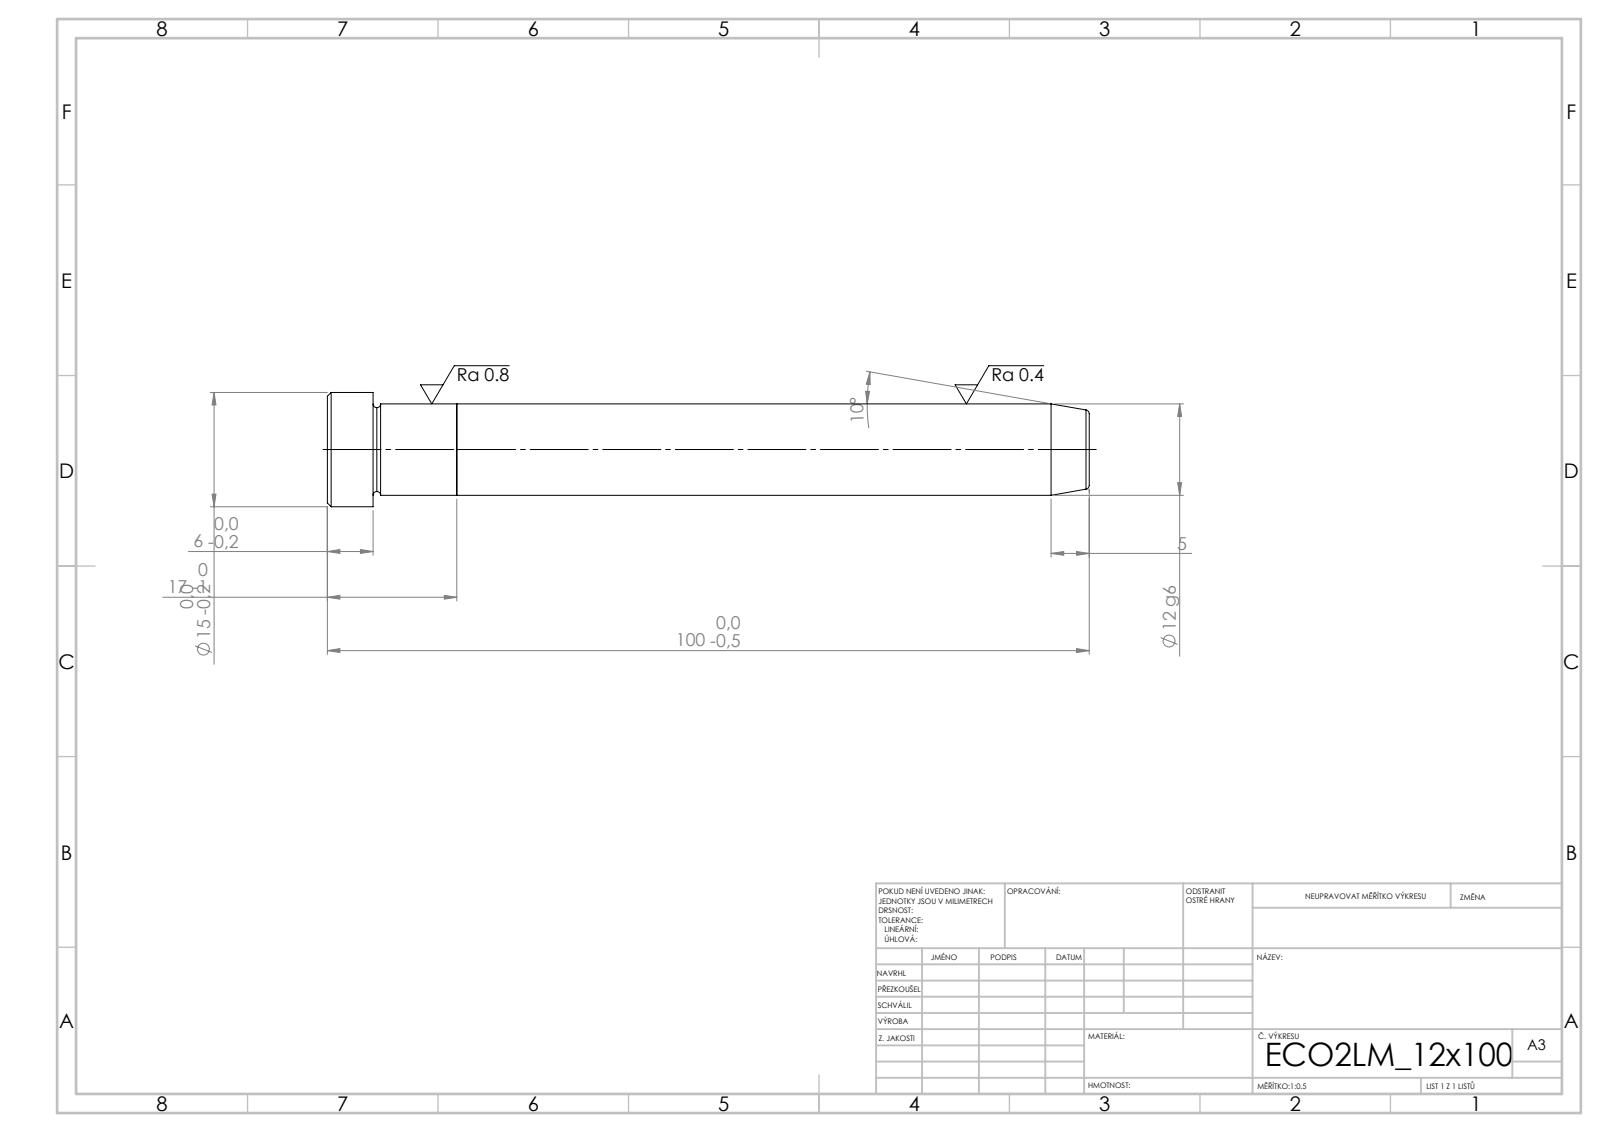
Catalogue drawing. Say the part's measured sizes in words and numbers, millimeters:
Its 3-D file was written by "SolidWorks 2019 (CONFIG_CONTROL_DESIGN)". It is 2 solids with 21 faces: 5 planar, 6 cylindrical and 10 other. Overall it measures 100 by 15 by 15 millimeters. Its volume is 11 591 cubic millimeters and its surface area 4 364 square millimeters. Round bosses or shafts: 1 of diameter 15, 1 of diameter 12. The main face-to-face distances are 17, 83, 100, 94, 11, 6.
